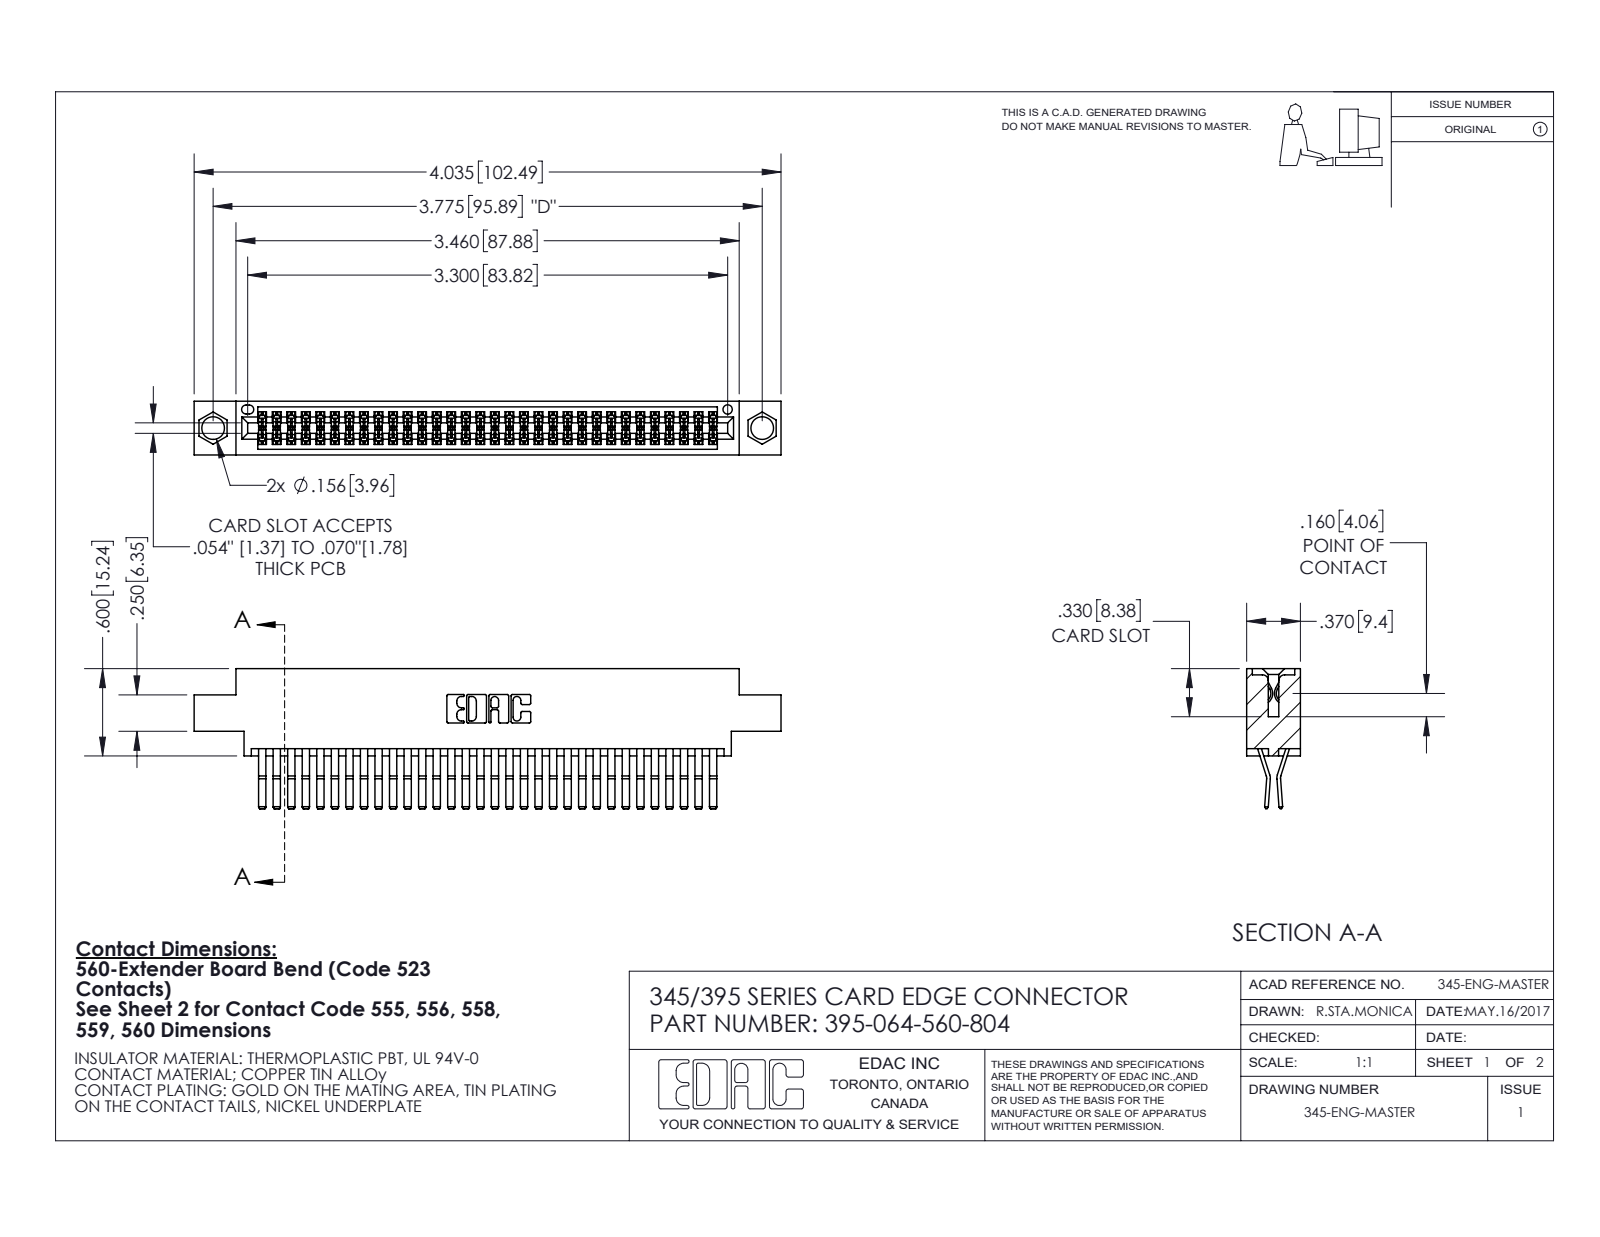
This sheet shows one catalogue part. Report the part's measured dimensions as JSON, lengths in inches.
{"part_name": "345 Part_0.170 Offset - 0.156 Dia-TI; 345-292-001_560 Tail; 395-064-560-804", "step_written_by": "SolidWorks 2020 (CONFIG_CONTROL_DESIGN)", "units": "inches", "bodies": {"solids": 65, "faces": 3472, "planar": 2210, "cylindrical": 1262, "other": 0}, "overall_size": [4.035, 0.962, 0.37], "volume_in3": 0.614, "surface_area_in2": 24.42, "round_holes": [[0.156, 2], [0.064, 1]], "partial_cylinders_radius": [[0.006, 96], [0.01, 22], [0.007, 6], [0.031, 6], [0.026, 3], [0.01, 2], [0.014, 2], [0.019, 2]], "face_to_face_distances": [0.025, 0.298, 0.072, 0.37, 0.2, 0.098, 0.272, 0.225, 0.175, 0.149], "hole_center_spacings": [0.27, 3.54, 3.775]}
